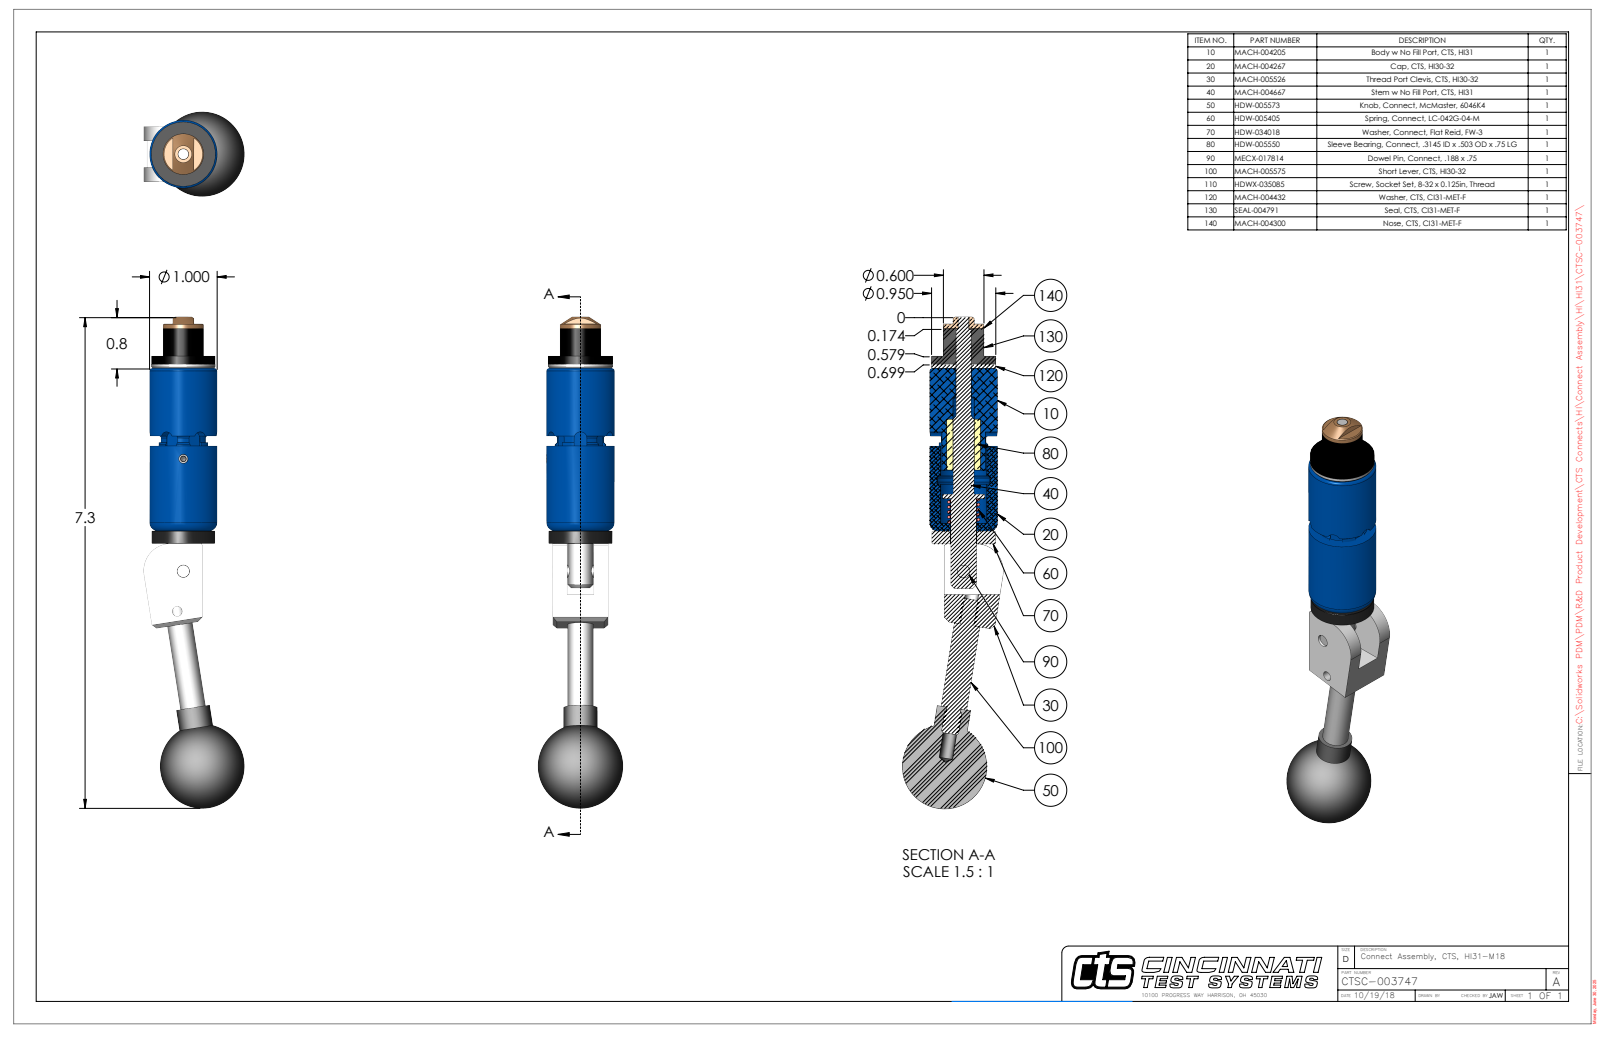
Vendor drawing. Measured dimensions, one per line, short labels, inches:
name: CTSC-003747
written by: SolidWorks 2023 (AUTOMOTIVE_DESIGN)
unit: in
bodies: 9 solids, 276 faces (107 planar, 109 cylindrical, 60 other)
size: 7.256 × 1.492 × 1.25
volume: 4.014 in³; area: 33.74 in²
holes: 2× ⌀0.201, 1× ⌀0.136, 1× ⌀0.15, 1× ⌀0.159, 1× ⌀0.189, 1× ⌀0.218, 1× ⌀0.228, 1× ⌀0.229, 1× ⌀0.385, 1× ⌀0.392, 1× ⌀0.688
bosses: 1× ⌀1, 1× ⌀0.95, 1× ⌀0.936, 1× ⌀0.6, 1× ⌀0.5, 1× ⌀0.38, 1× ⌀0.375, 1× ⌀0.25
rounds: 6× R0.093, 2× R0.029, 1× R0.375, 1× R0.4, 1× R0.447
face distances: 0.06, 0.21, 0.602, 2.46, 2.4, 0.812, 2.647, 2.587, 0.187, 0.391
hole spacings: 0.599, 1.658, 2.252
